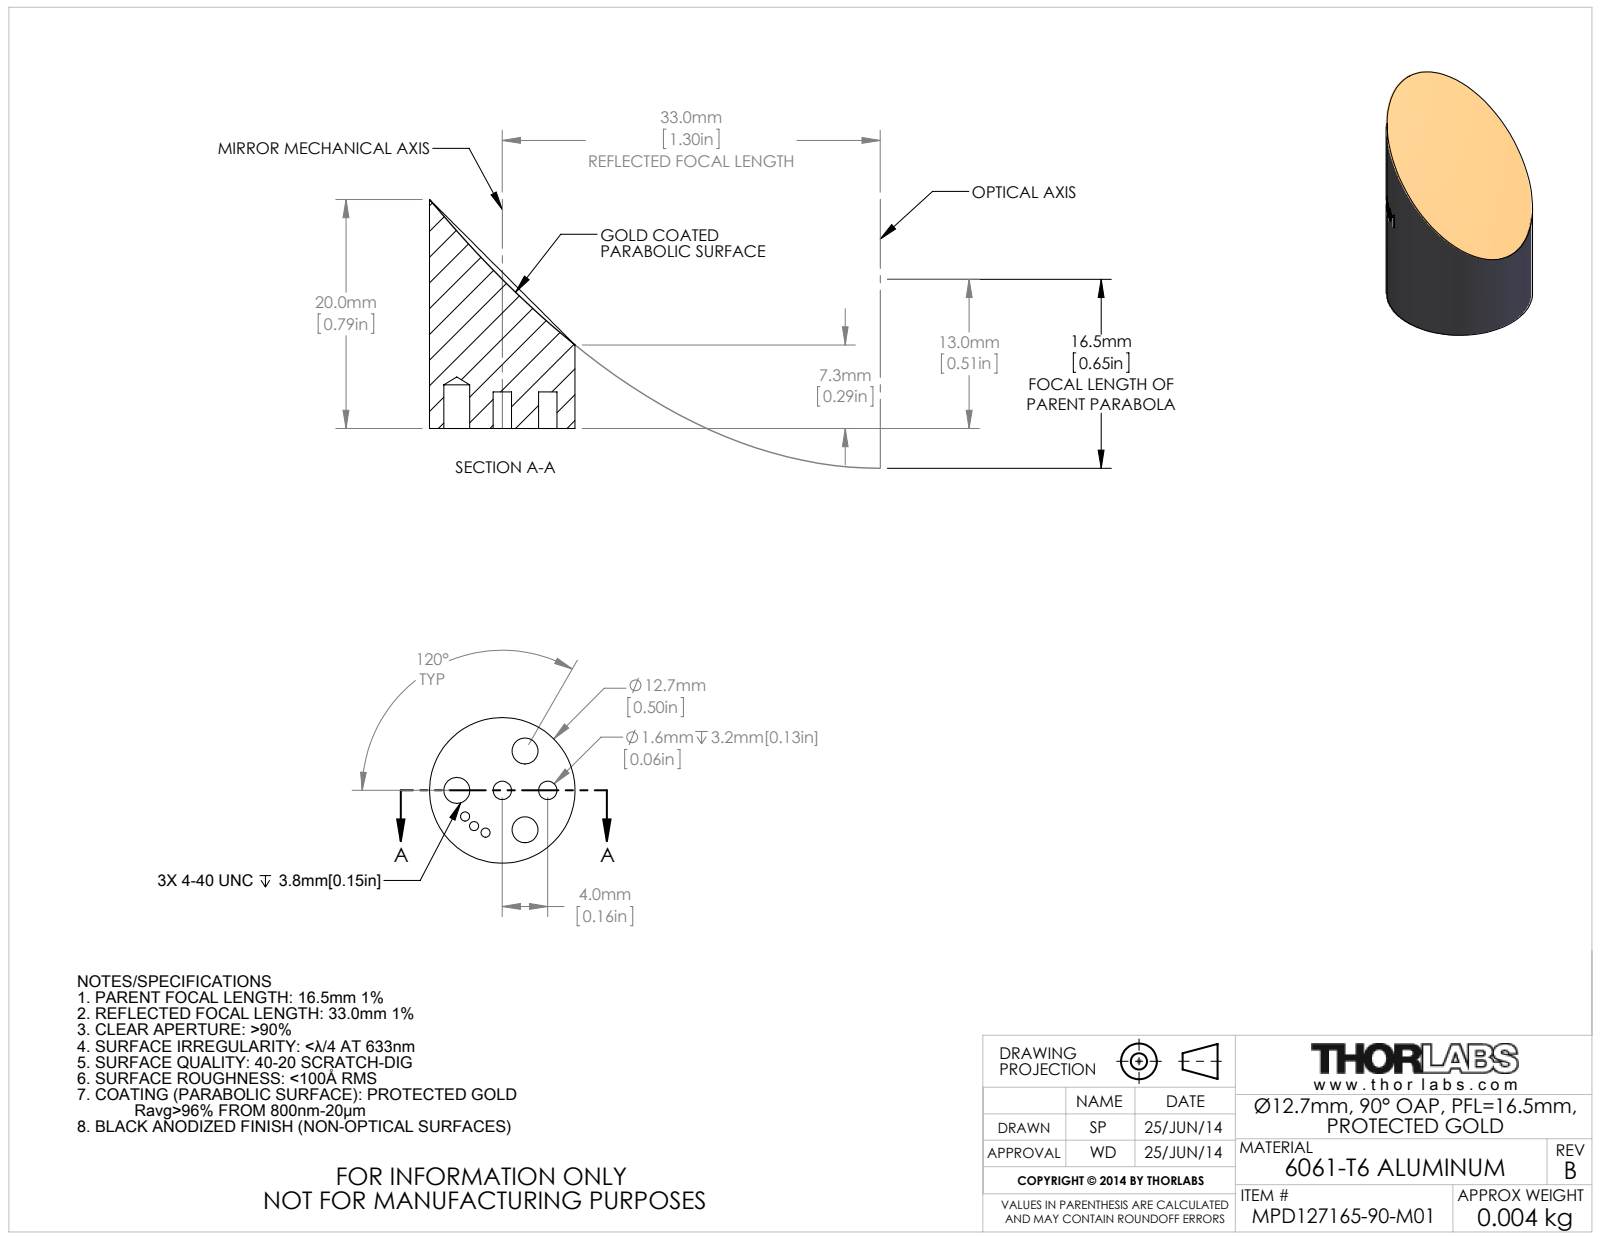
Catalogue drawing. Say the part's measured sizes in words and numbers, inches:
The part is named "TTN006723-E0W". Its 3-D file was written by "SolidWorks 2014 (CONFIG_CONTROL_DESIGN)". It is 1 solid with 64 faces: 3 planar, 47 cylindrical and 14 other. Overall it measures 0.787 by 0.5 by 0.5 inches. Its volume is 0.099 cubic inches and its surface area 1.497 square inches. Round holes: 3 of diameter 0.089, 2 of diameter 0.063. Round bosses or shafts: 1 of diameter 0.5. The main face-to-face distances are 0.125. The hole center spacings are 0.156, 0.271, 0.156, 0.27, 0.313.
